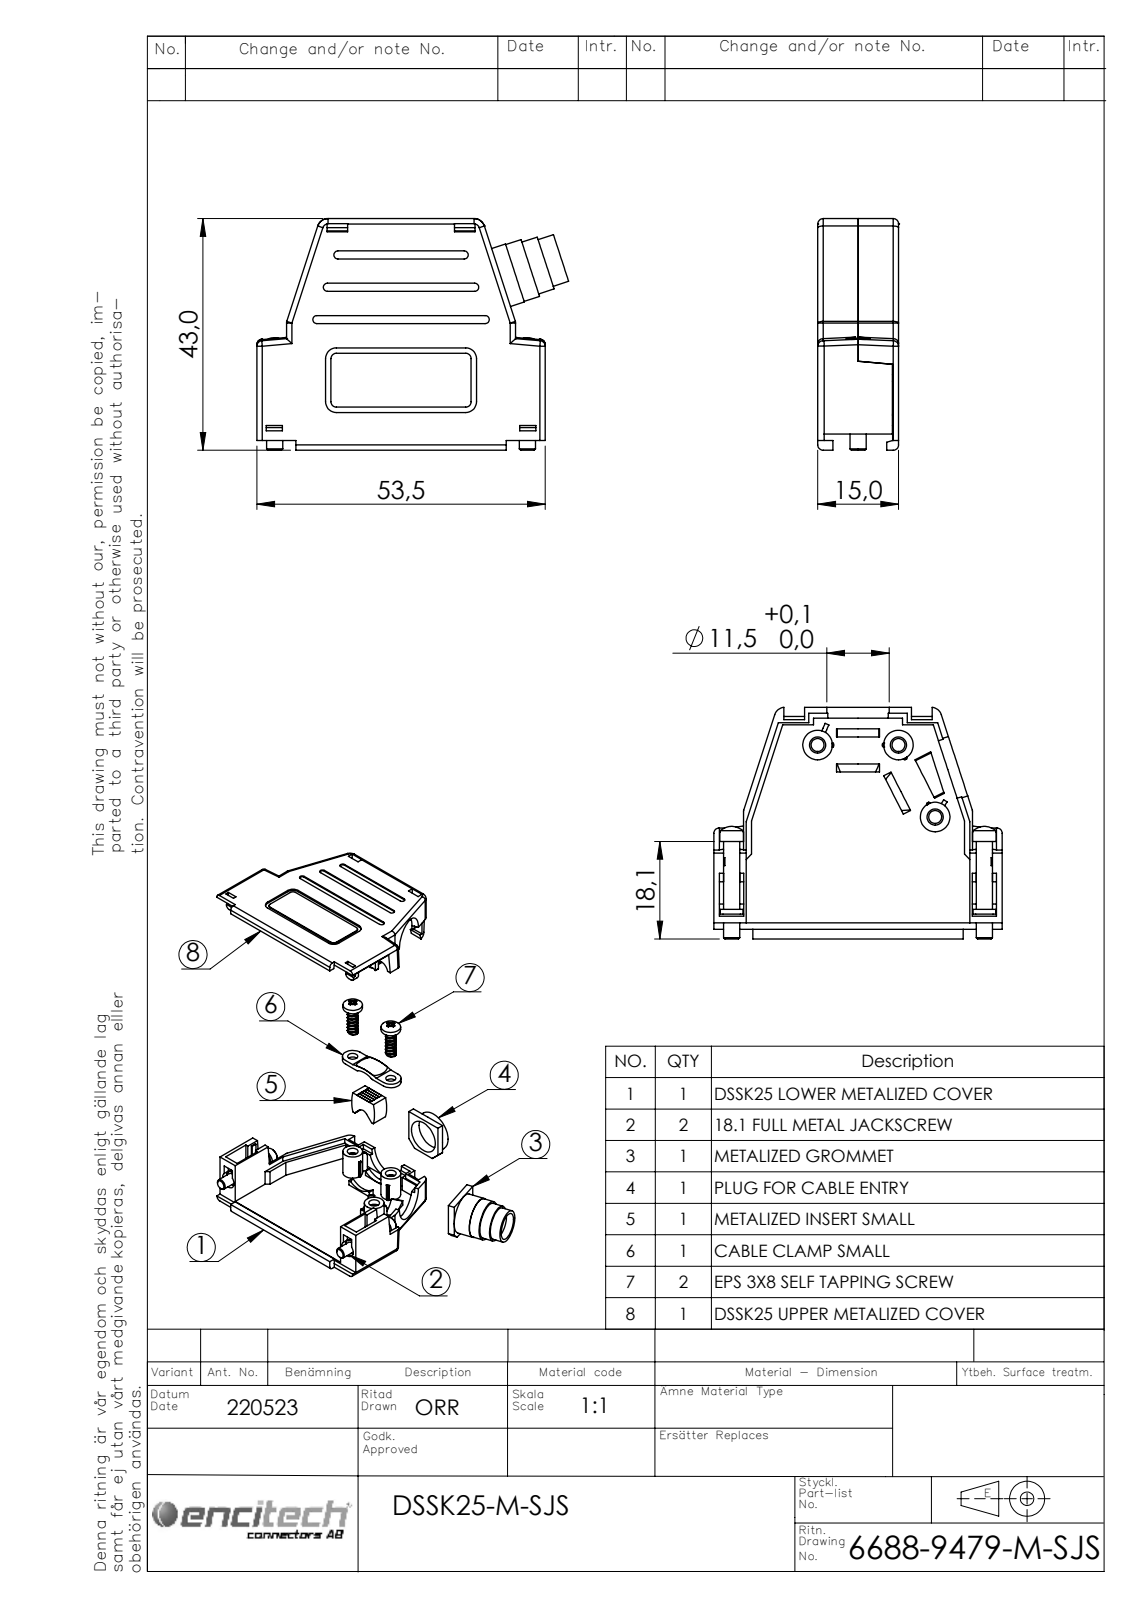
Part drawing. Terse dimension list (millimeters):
name: 6855-0109-01; 6822-0121-32; 6826-0133-01; 6822-0128-32 (+5 more)
written by: SolidWorks 2021 (AUTOMOTIVE_DESIGN)
unit: mm
bodies: 12 solids, 814 faces (528 planar, 225 cylindrical, 61 other)
size: 57.84 × 43 × 15
volume: 10 749 mm³; area: 16 268 mm²
holes: 3× ⌀2.4, 3× ⌀3, 2× ⌀2.8, 2× ⌀11.6, 1× ⌀3.5, 1× ⌀7.5, 1× ⌀8.5, 1× ⌀9.4, 1× ⌀9.5, 1× ⌀10.5
bosses: 3× ⌀5.5, 2× ⌀5.45, 2× ⌀4.4, 2× ⌀4.2, 2× ⌀3, 2× ⌀2.46, 1× ⌀11.4, 1× ⌀11.3
rounds: 40× R1, 14× R2, 6× R0.75, 5× R5.8, 4× R0.1, 4× R0.25, 4× R0.5, 2× R1.2
face distances: 1.7, 13.3, 11.6, 15, 1.5, 2, 14.8, 13.1, 3, 5.8
hole spacings: 7.57, 15, 18.92, 25.58
